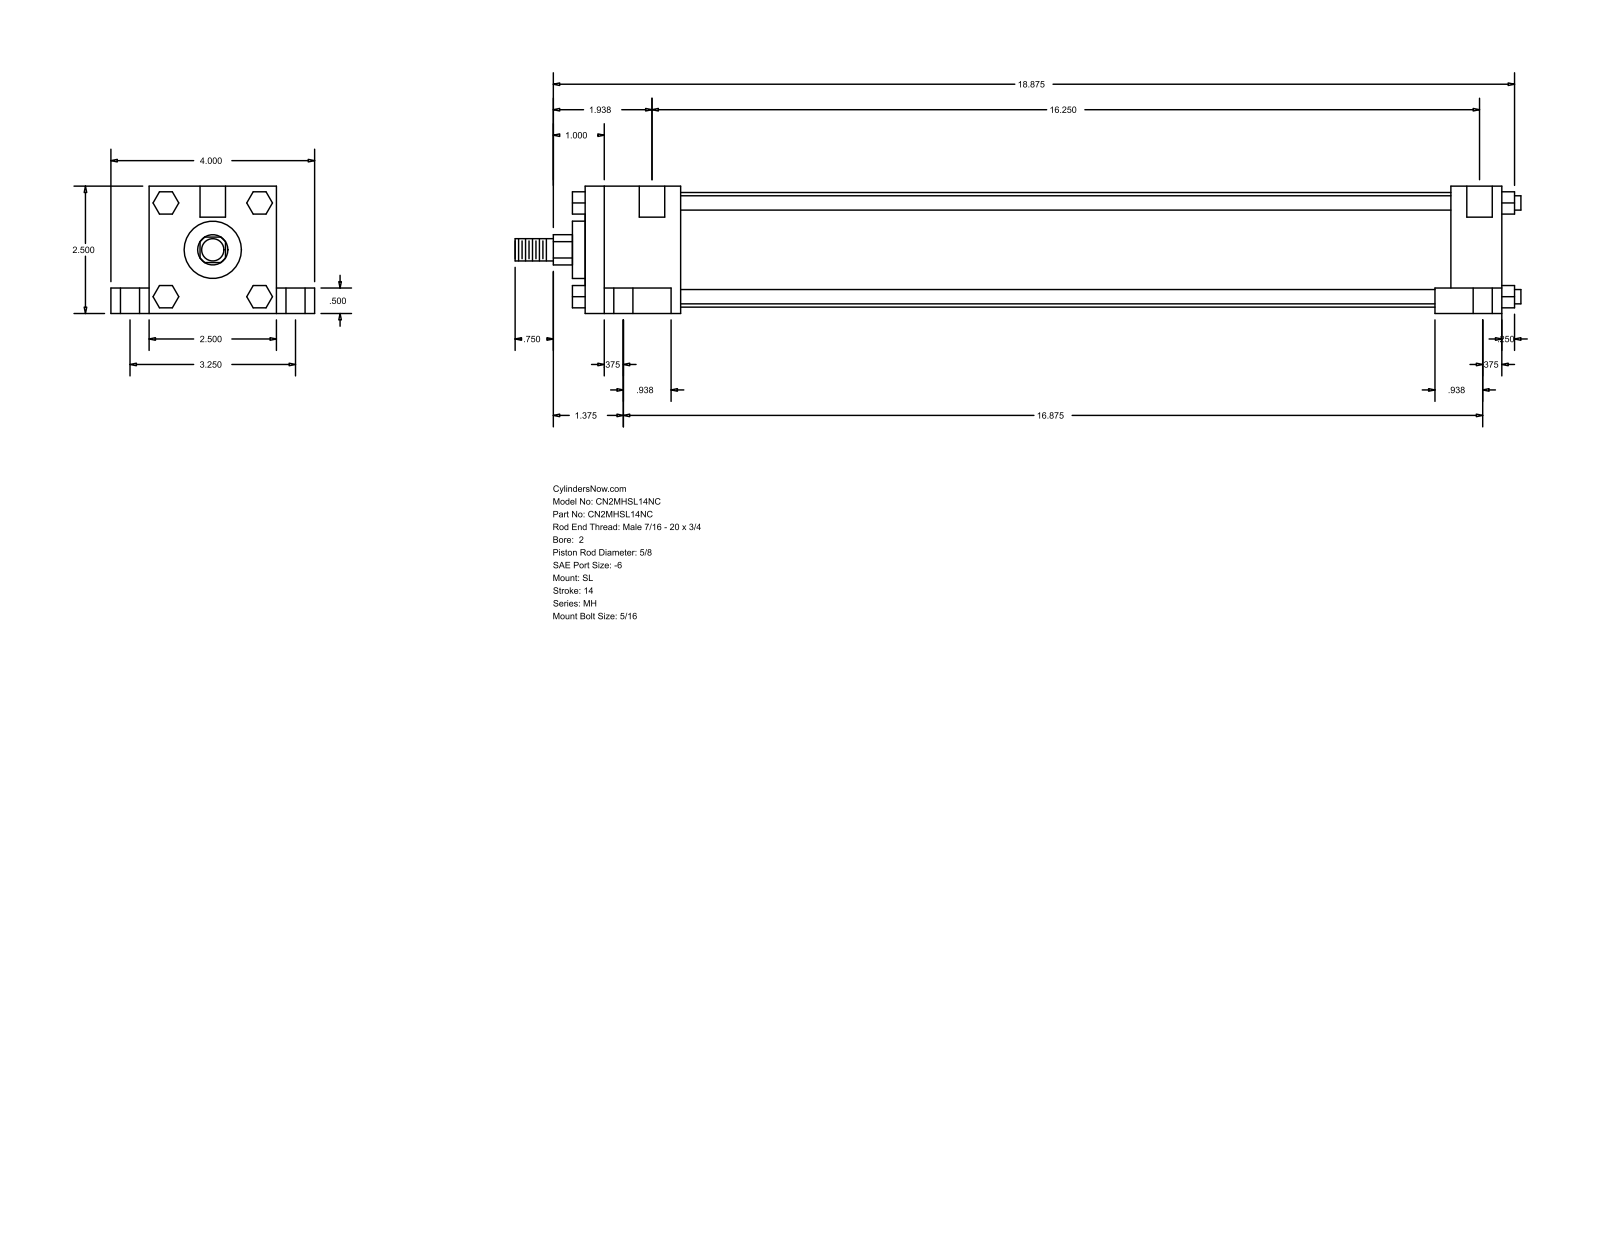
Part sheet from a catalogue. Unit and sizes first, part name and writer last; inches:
Units: inches
Overall size (bounding box): 19.75 × 4 × 2.5
Round holes (diameter × count): ⌀0.219 ×4, ⌀0.375 ×4, ⌀0.625 ×4, ⌀0.5 ×2
Round bosses / shafts (diameter × count): ⌀0.281 ×4, ⌀2.25 ×1, ⌀1.125 ×1, ⌀0.625 ×1, ⌀0.437 ×1
Partial cylindrical surfaces — rounded edges, fillets, slot ends (radius × count): R0.297 ×1
Main face-to-face distances: 2.5, 18, 0.5, 0.75, 3.25, 2, 17, 1, 1.875, 15.125
Hole centre spacings: 1.626, 1.668, 1.719, 3.25, 16.393, 16.563, 16.58, 16.875
Bodies: 0 solids, 148 faces (112 planar, 36 cylindrical, 0 other)
Part name (STEP PRODUCT): MH_SL__0200_0.625
STEP written by: GSSL Pune (CONFIG_CONTROL_DESIGN)
